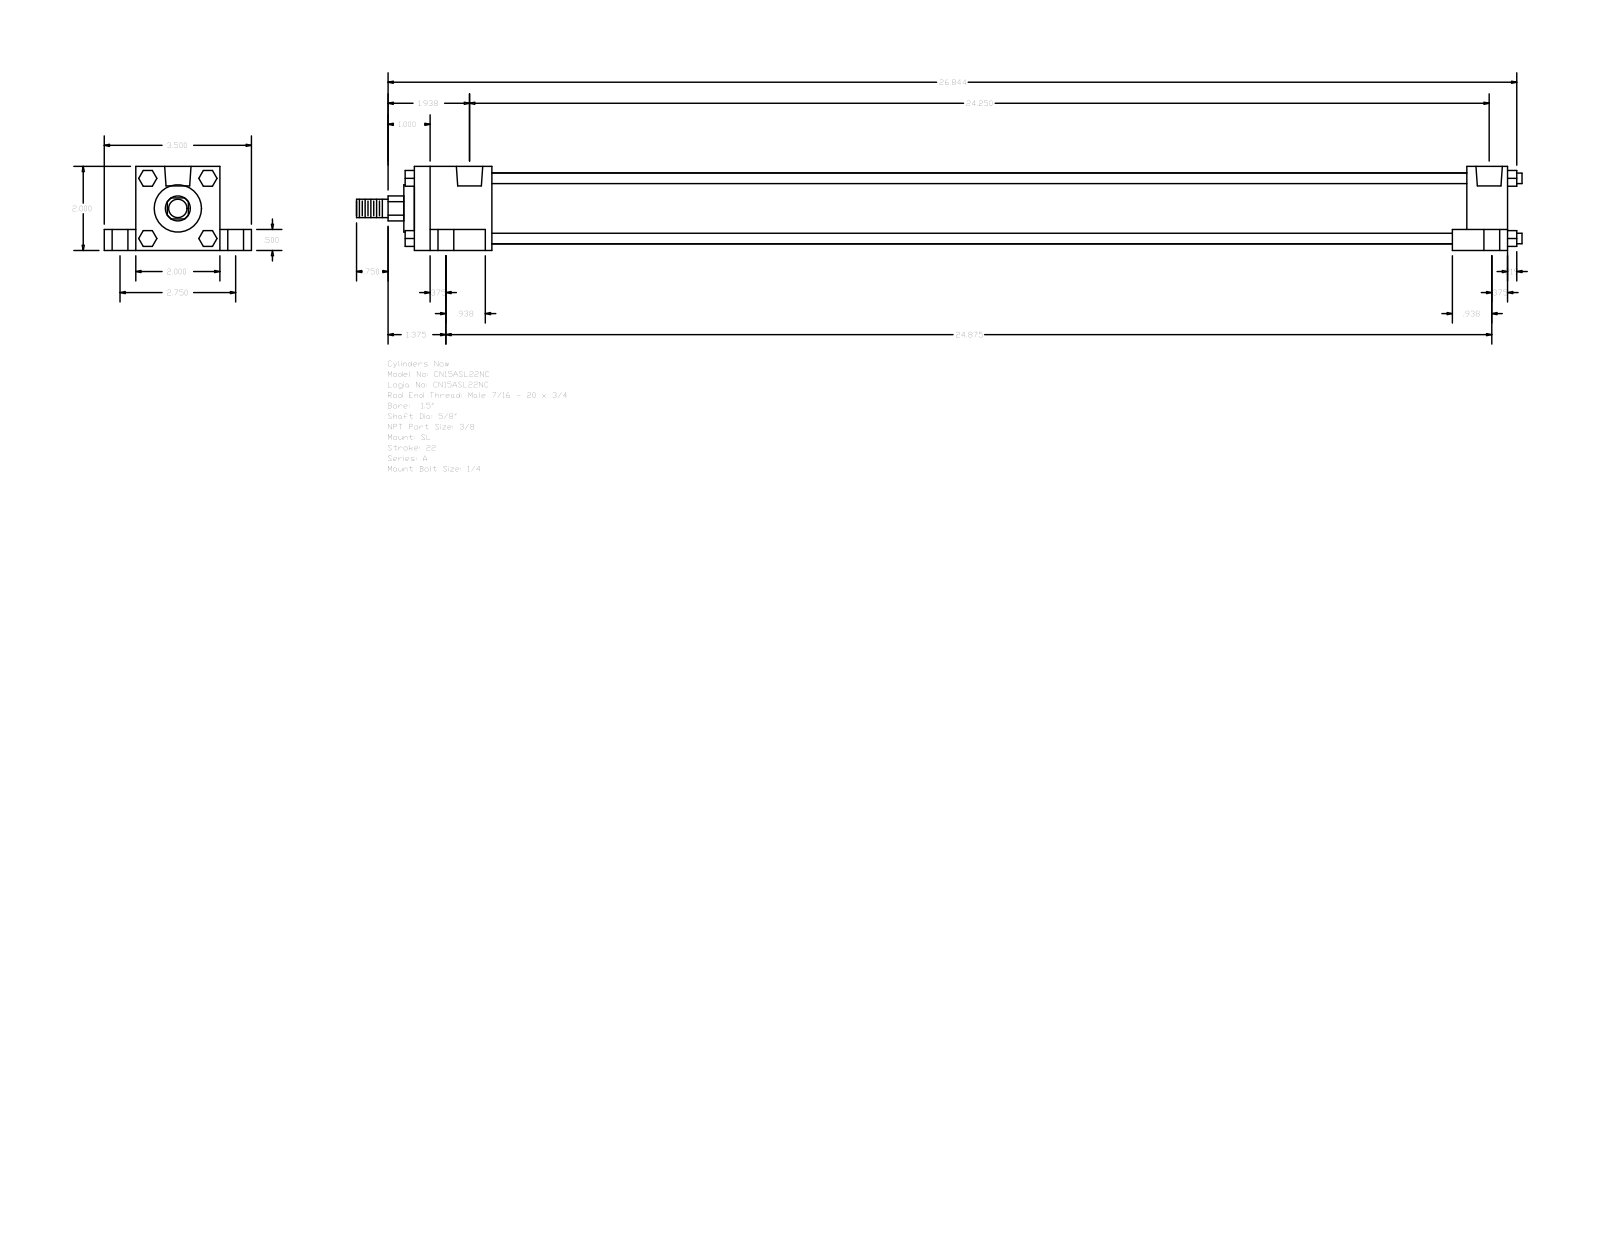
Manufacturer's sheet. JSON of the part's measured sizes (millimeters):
{"part_name": "A_SL__0150_0.625", "step_written_by": "GSSL Pune (CONFIG_CONTROL_DESIGN)", "units": "millimeters", "bodies": {"solids": 0, "faces": 148, "planar": 112, "cylindrical": 36, "other": 0}, "overall_size": [704.06, 88.9, 50.8], "round_holes": [[5.56, 4], [9.53, 4], [15.88, 4], [15.93, 2]], "round_bosses_or_shafts": [[6.35, 4], [42.93, 1], [28.57, 1], [15.88, 1], [11.11, 1]], "partial_cylinders_radius": [[7.54, 1]], "face_to_face_distances": [50.8, 19.05, 38.1, 12.7, 69.85, 660.39, 9.52, 635.79, 24.6, 46.83], "hole_center_spacings": [3.97, 34.96, 35.36, 37.73, 39.41, 69.84, 608.01, 611.98]}
